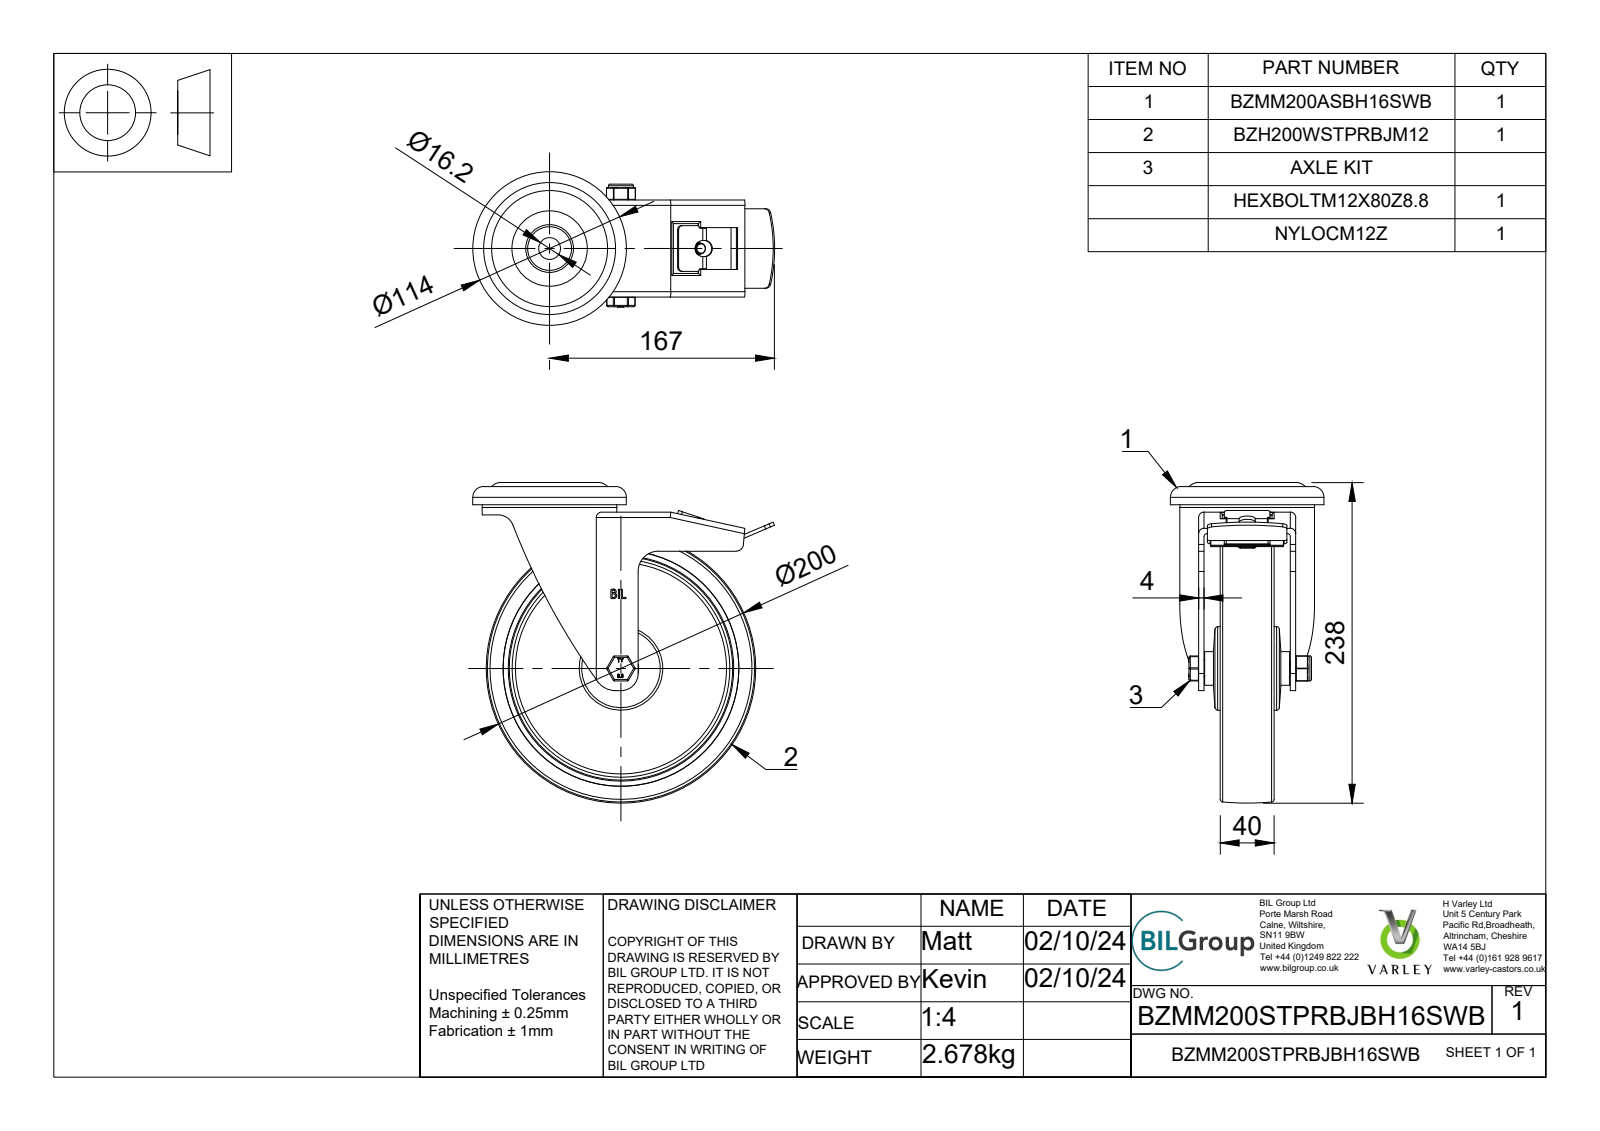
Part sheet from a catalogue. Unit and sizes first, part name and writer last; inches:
Units: inches
Overall size (bounding box): 9.37 × 8.819 × 4.488
Round holes (diameter × count): ⌀0.315 ×1, ⌀0.472 ×1, ⌀0.48 ×1, ⌀0.496 ×1, ⌀0.551 ×1, ⌀0.638 ×1, ⌀0.787 ×1, ⌀1.122 ×1, ⌀1.213 ×1, ⌀1.587 ×1, ⌀1.594 ×1, ⌀1.614 ×1
Round bosses / shafts (diameter × count): ⌀4.488 ×1, ⌀3.937 ×1, ⌀2.913 ×1, ⌀2.441 ×1, ⌀2.224 ×1, ⌀1.89 ×1, ⌀1.85 ×1, ⌀1.606 ×1
Partial cylindrical surfaces — rounded edges, fillets, slot ends (radius × count): R0.039 ×37, R0.02 ×23, R0.079 ×12, R0.157 ×7, R0.059 ×6, R0.118 ×2, R0.236 ×2, R0.217 ×1
Main face-to-face distances: 0.256, 0.915, 0.157, 0.659, 0.472, 0.63, 1.289, 1.545, 2.205, 2.677
Volume: 53.09 in³ · Surface area: 522.4 in²
Bodies: 25 solids, 956 faces (405 planar, 253 cylindrical, 298 other)
Part name (STEP PRODUCT): BZMM200STPRBJBH16SWB v2; BZMM200ASBH16SWB - 64 v1; ZINC PLATED, PRESSED STEEL HEAD; ZINC PLATED, PRESSED STEEL FORKS (+8 more)
STEP written by: Autodesk Translation Framework v13.20.0.188 (AUTOMOTIVE_DESIGN)
